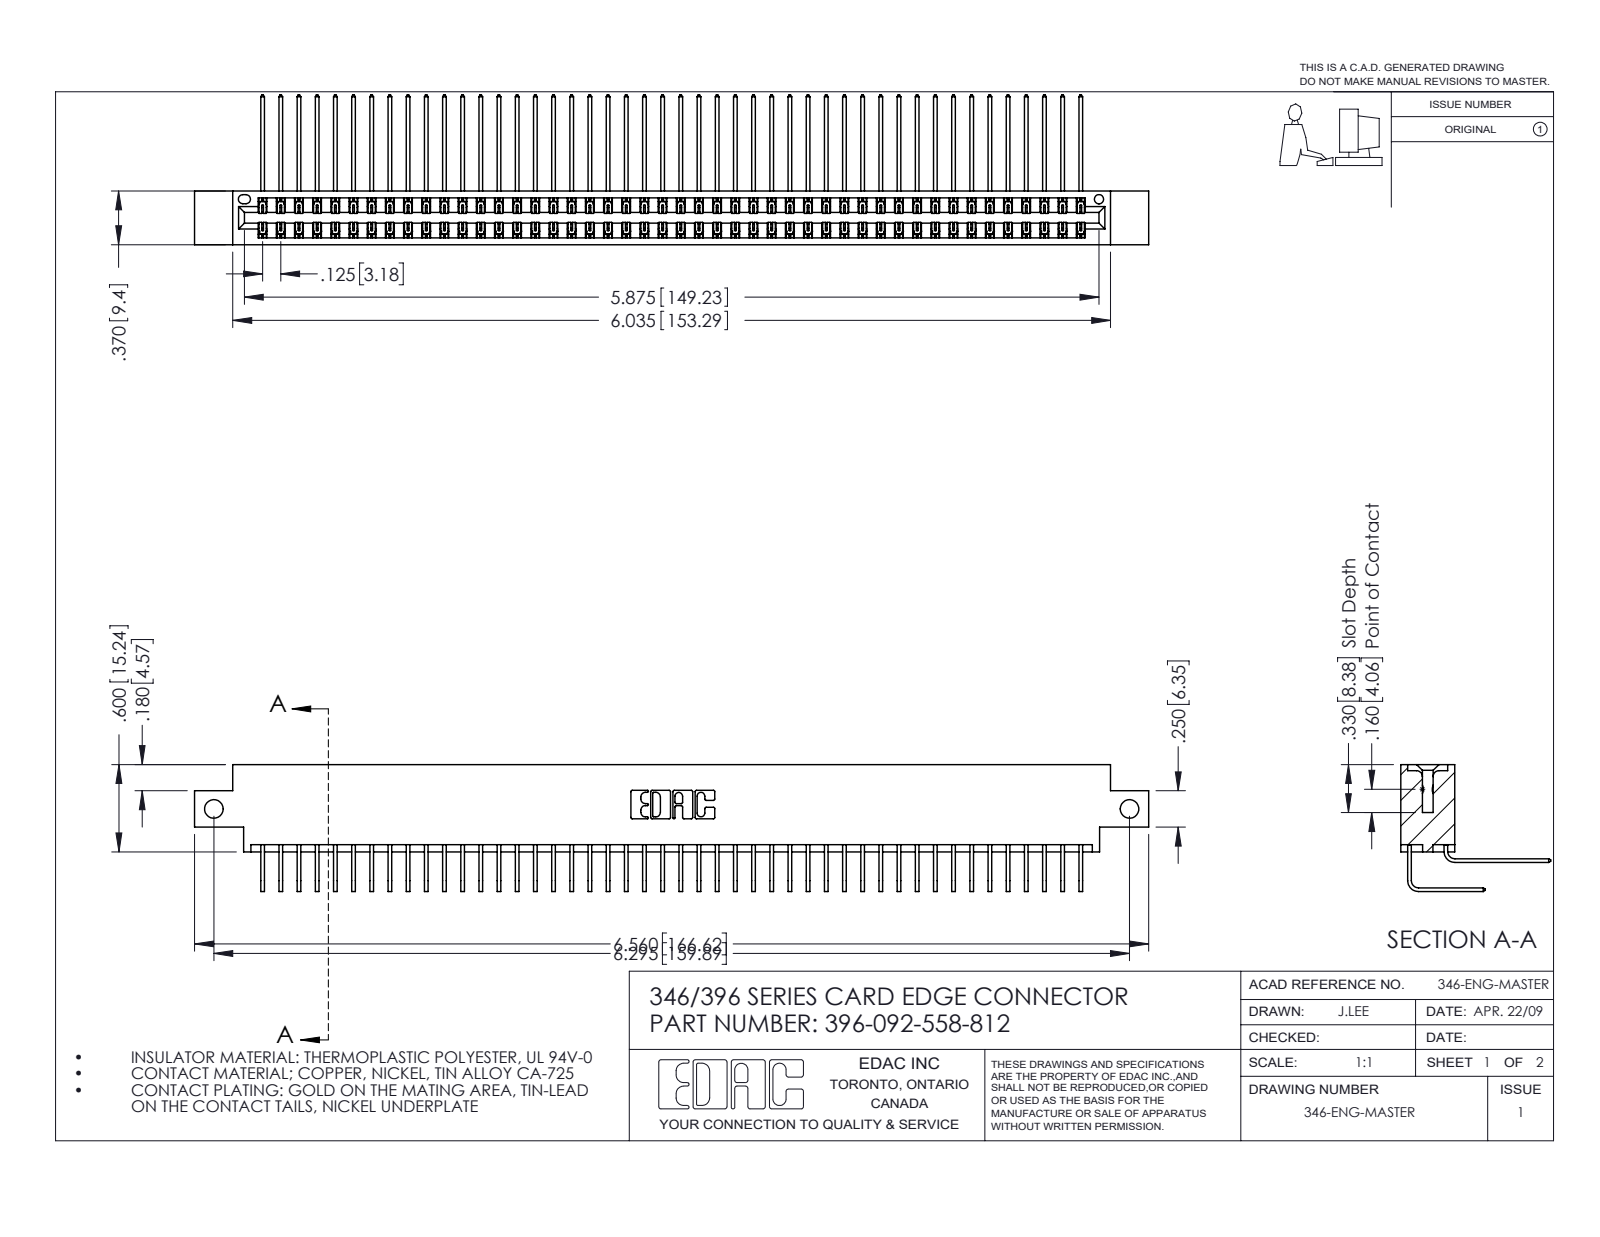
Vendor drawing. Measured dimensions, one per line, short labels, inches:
name: 345-292-001_558 Tail - 2; 396-092-558-812; 345-292-001_558 559 Tail - 1; 346 Part_0.170 Offset - Side Mount
written by: SolidWorks 2016 (CONFIG_CONTROL_DESIGN)
unit: in
bodies: 93 solids, 5094 faces (3484 planar, 1610 cylindrical, 0 other)
size: 6.56 × 1.03 × 0.873
volume: 1.011 in³; area: 39.41 in²
holes: 2× ⌀0.128, 1× ⌀0.064
rounds: 138× R0.006, 22× R0.01, 6× R0.007, 6× R0.031, 3× R0.026, 2× R0.014, 2× R0.022, 2× R0.024
face distances: 0.322, 0.048, 0.025, 0.37, 0.25, 0.298, 0.072, 0.275, 0.148, 0.222
hole spacings: 6.295
